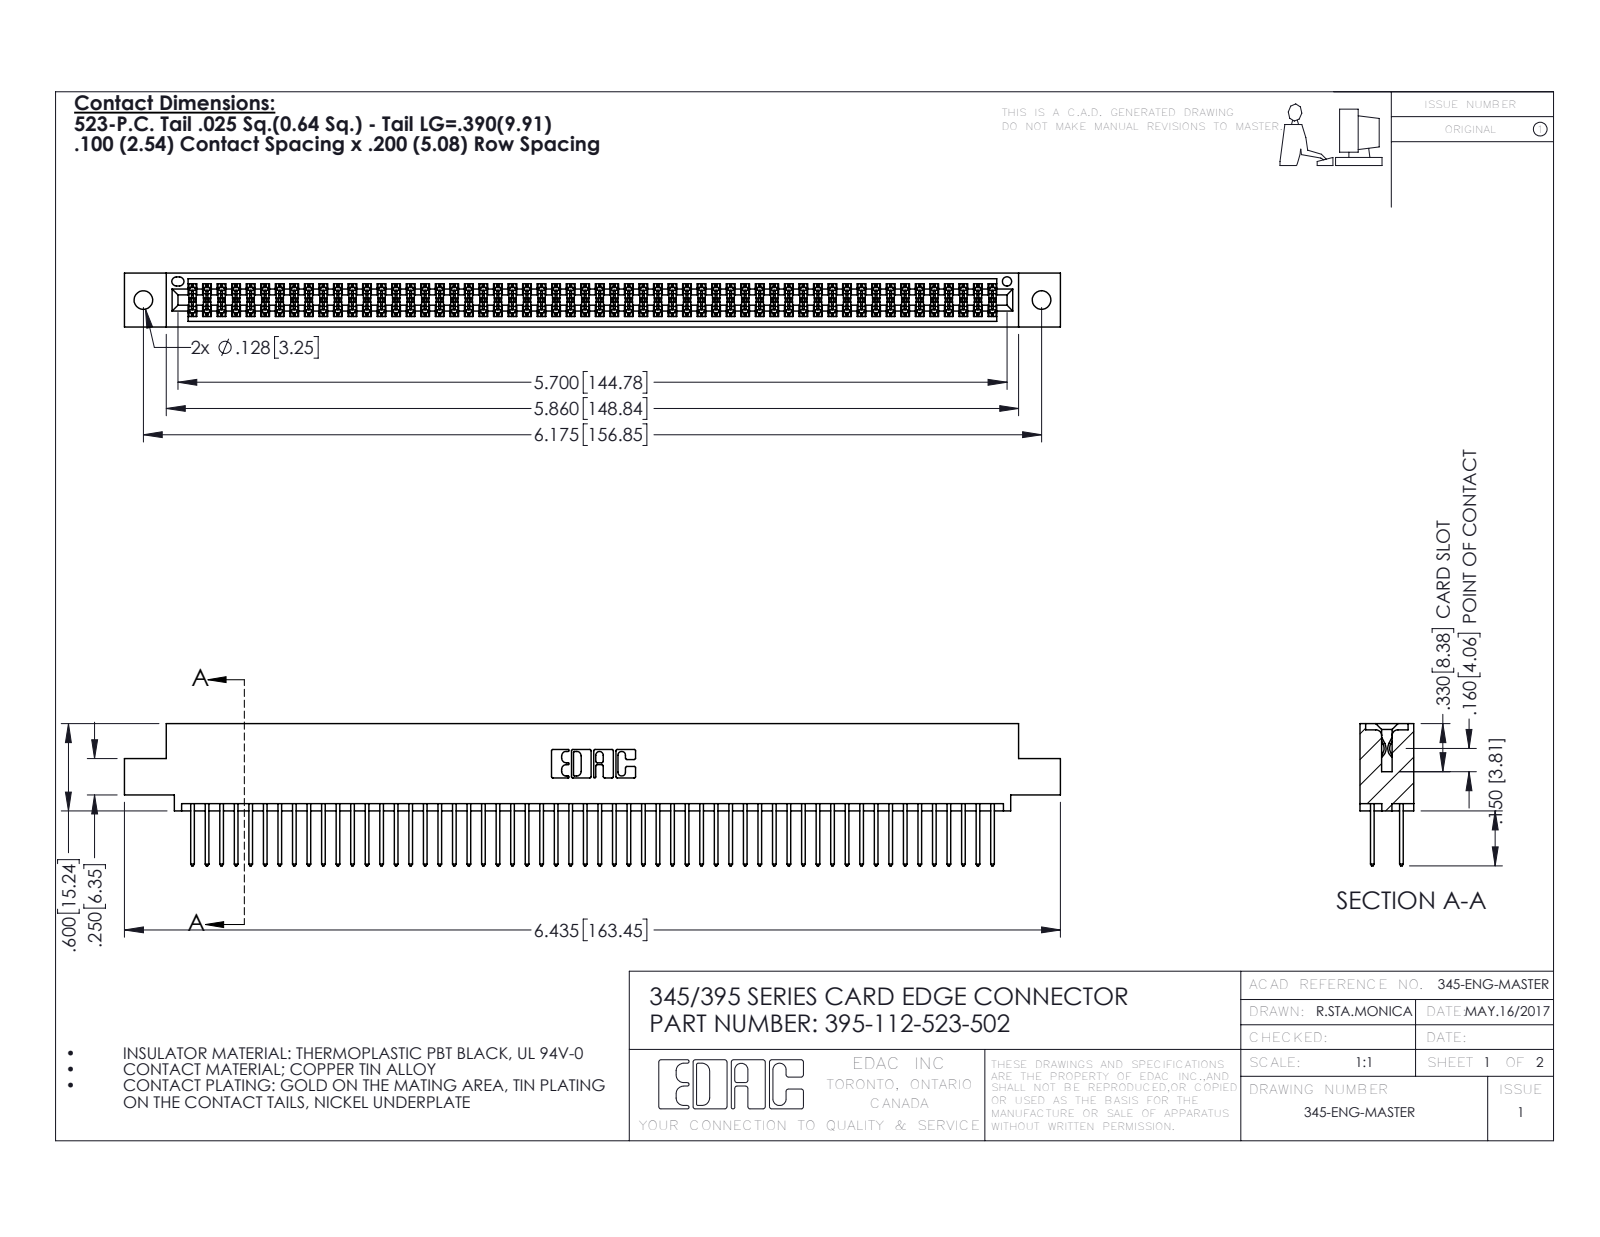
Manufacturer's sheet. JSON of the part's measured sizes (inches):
{"part_name": "395-112-523-502; 345 Part_0.110 Offset - 0.128 Dia; 345-292-001_345-293-123", "step_written_by": "SolidWorks 2016 (CONFIG_CONTROL_DESIGN)", "units": "inches", "bodies": {"solids": 113, "faces": 5730, "planar": 3780, "cylindrical": 1950, "other": 0}, "overall_size": [6.435, 0.977, 0.37], "volume_in3": 0.984, "surface_area_in2": 38.69, "round_holes": [[0.128, 2], [0.064, 1]], "partial_cylinders_radius": [[0.006, 168], [0.01, 112], [0.01, 22], [0.007, 6], [0.031, 6], [0.026, 3], [0.014, 2], [0.019, 2]], "face_to_face_distances": [0.072, 0.298, 0.2, 0.098, 0.272, 0.025, 0.37, 0.225, 0.175, 0.149], "hole_center_spacings": [0.27, 5.939, 6.175]}
